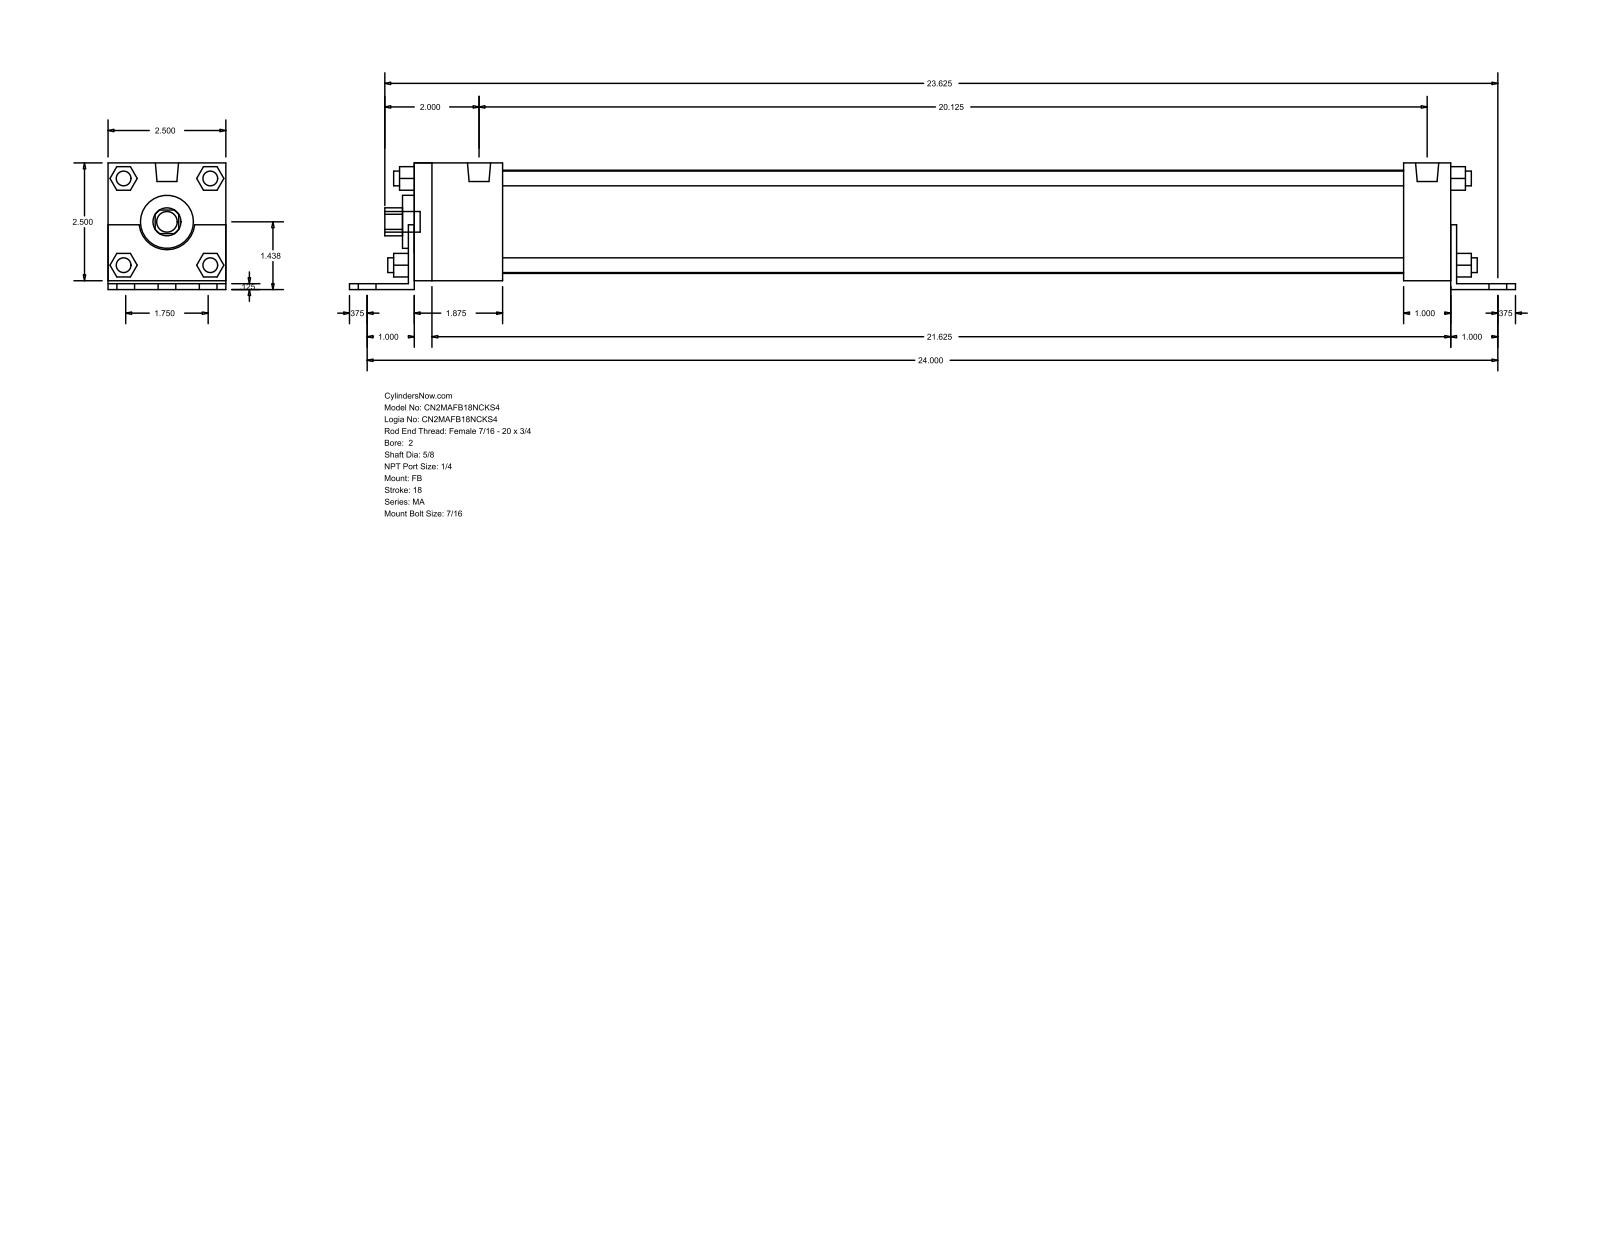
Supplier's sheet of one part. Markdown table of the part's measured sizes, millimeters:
| quantity | value |
| --- | --- |
| part name | MA_FB__0200_0.625 |
| STEP written by | GSSL Pune (CONFIG_CONTROL_DESIGN) |
| units | millimeters |
| bodies | 0 solids, 140 faces (105 planar, 35 cylindrical, 0 other) |
| overall size | 628.65 × 68.26 × 63.5 |
| round holes (diameter × count) | 15.88 × 1, 28.57 × 1, 55.63 × 1 |
| round bosses / shafts (diameter × count) | 7.94 × 8, 11.11 × 7, 12.49 × 2 |
| partial cylindrical surfaces (radius × count) | 7.54 × 1, 15.05 × 1 |
| main face-to-face distances | 63.5, 4.76, 3.17, 68.26, 1.59, 3.18, 65.09, 561.97, 558.79, 25.4 |
